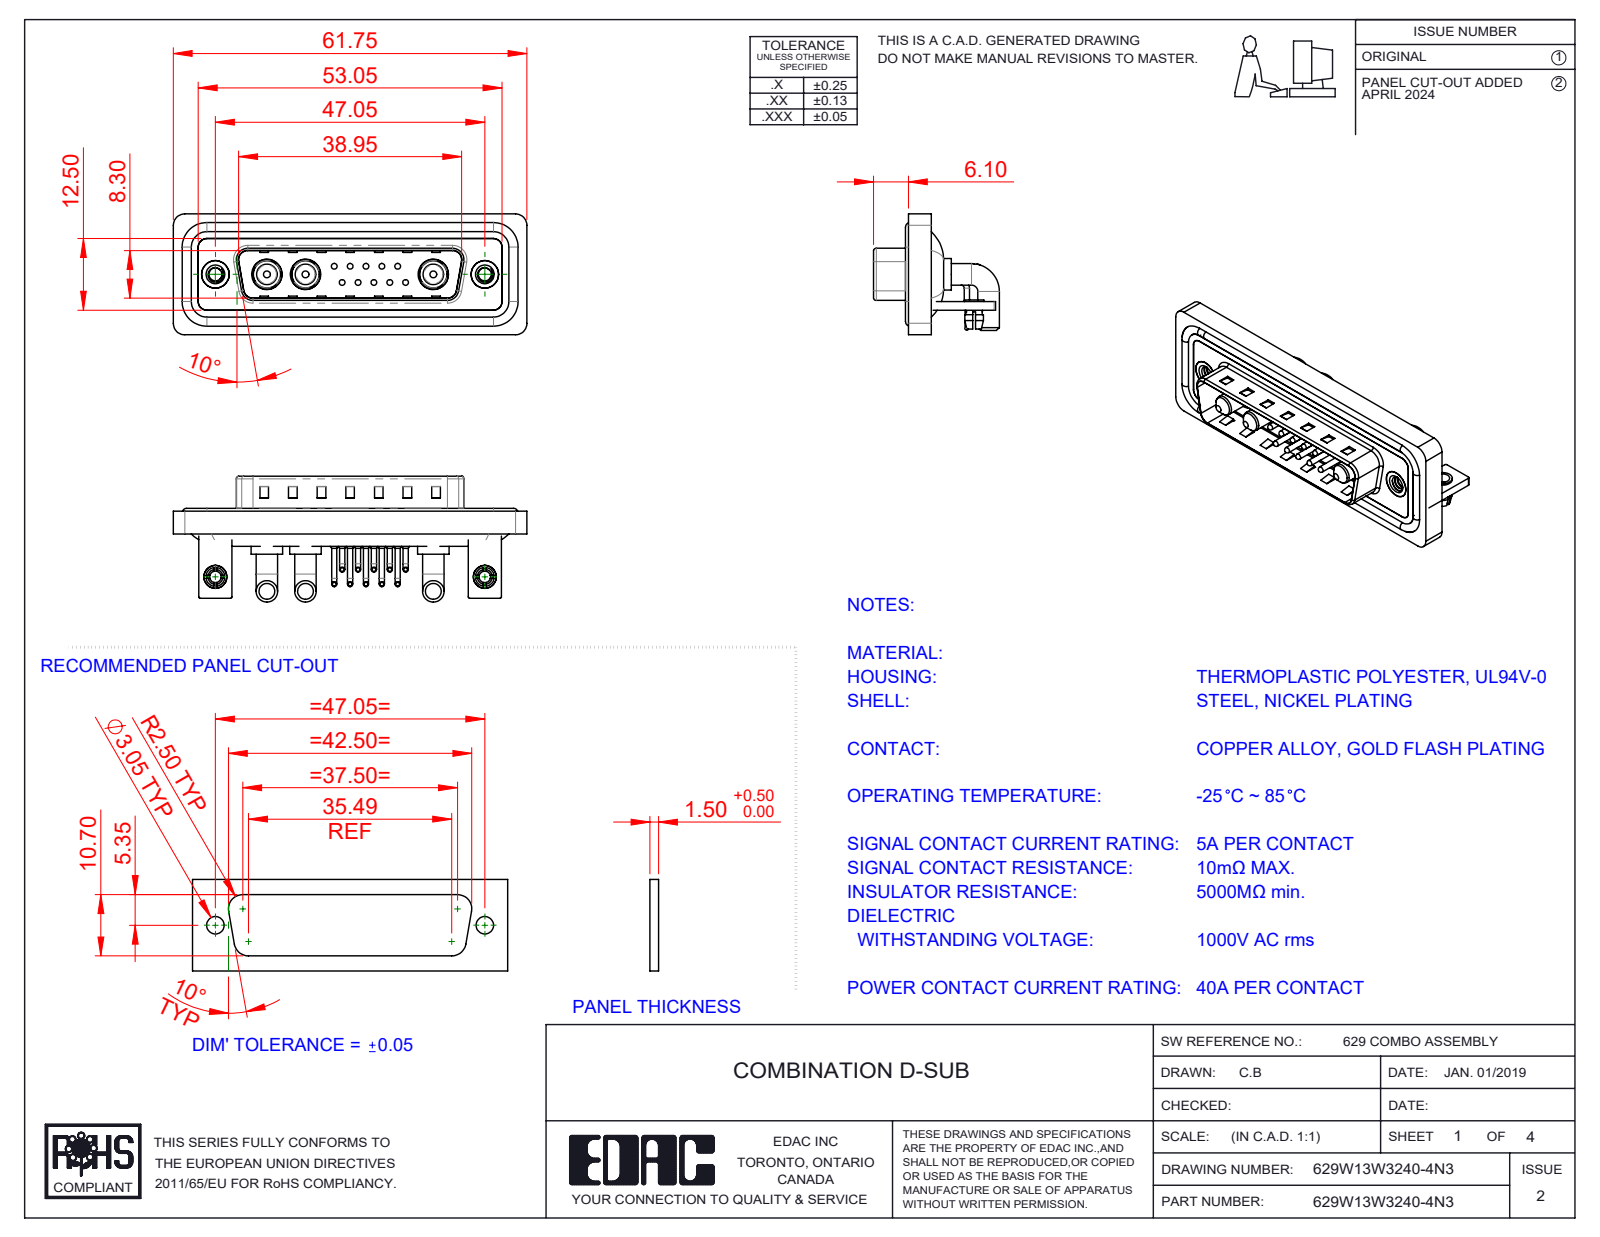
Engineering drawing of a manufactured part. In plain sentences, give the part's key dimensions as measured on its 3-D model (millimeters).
The part is named "629Combo Threaded Rivet_3; 629Combo Stabilizer Bracket; 629Combo Waterproof Housing_25 Contacts; 629Combo Contact Row 1 (+7 more)". Its 3-D file was written by "SolidWorks 2023 (CONFIG_CONTROL_DESIGN)". It is 27 solids with 1844 faces: 947 planar, 661 cylindrical and 236 other. Overall it measures 61.75 by 21.98 by 21.1 millimeters. Its volume is 8 143 cubic millimeters and its surface area 13 425 square millimeters. Round holes: 12 of diameter 2, 10 of diameter 0.75, 10 of diameter 1.6, 3 of diameter 4.85, 3 of diameter 5.3, 2 of diameter 2.26, 2 of diameter 2.5, 2 of diameter 3.2, 2 of diameter 4, 2 of diameter 4.8, 2 of diameter 5. Round bosses or shafts: 20 of diameter 0.9, 10 of diameter 1.5, 10 of diameter 1, 10 of diameter 0.65, 6 of diameter 3.75, 4 of diameter 1.6, 3 of diameter 5.5, 3 of diameter 5.2. Partial cylindrical surfaces (rounded edges, fillets, slot ends): 19 of radius 2, 18 of radius 1.5, 16 of radius 0.25, 10 of radius 1.01, 9 of radius 0.5, 8 of radius 1.6, 4 of radius 0.6, 4 of radius 0.65. The main face-to-face distances are 0.4, 0.8, 1.5, 2.9, 2.1, 1.1, 4.1, 1.6, 3.7, 4.5. The hole center spacings are 3.16, 2.77, 5.04, 5.54, 7.49, 5.03, 8.31, 10.11.
